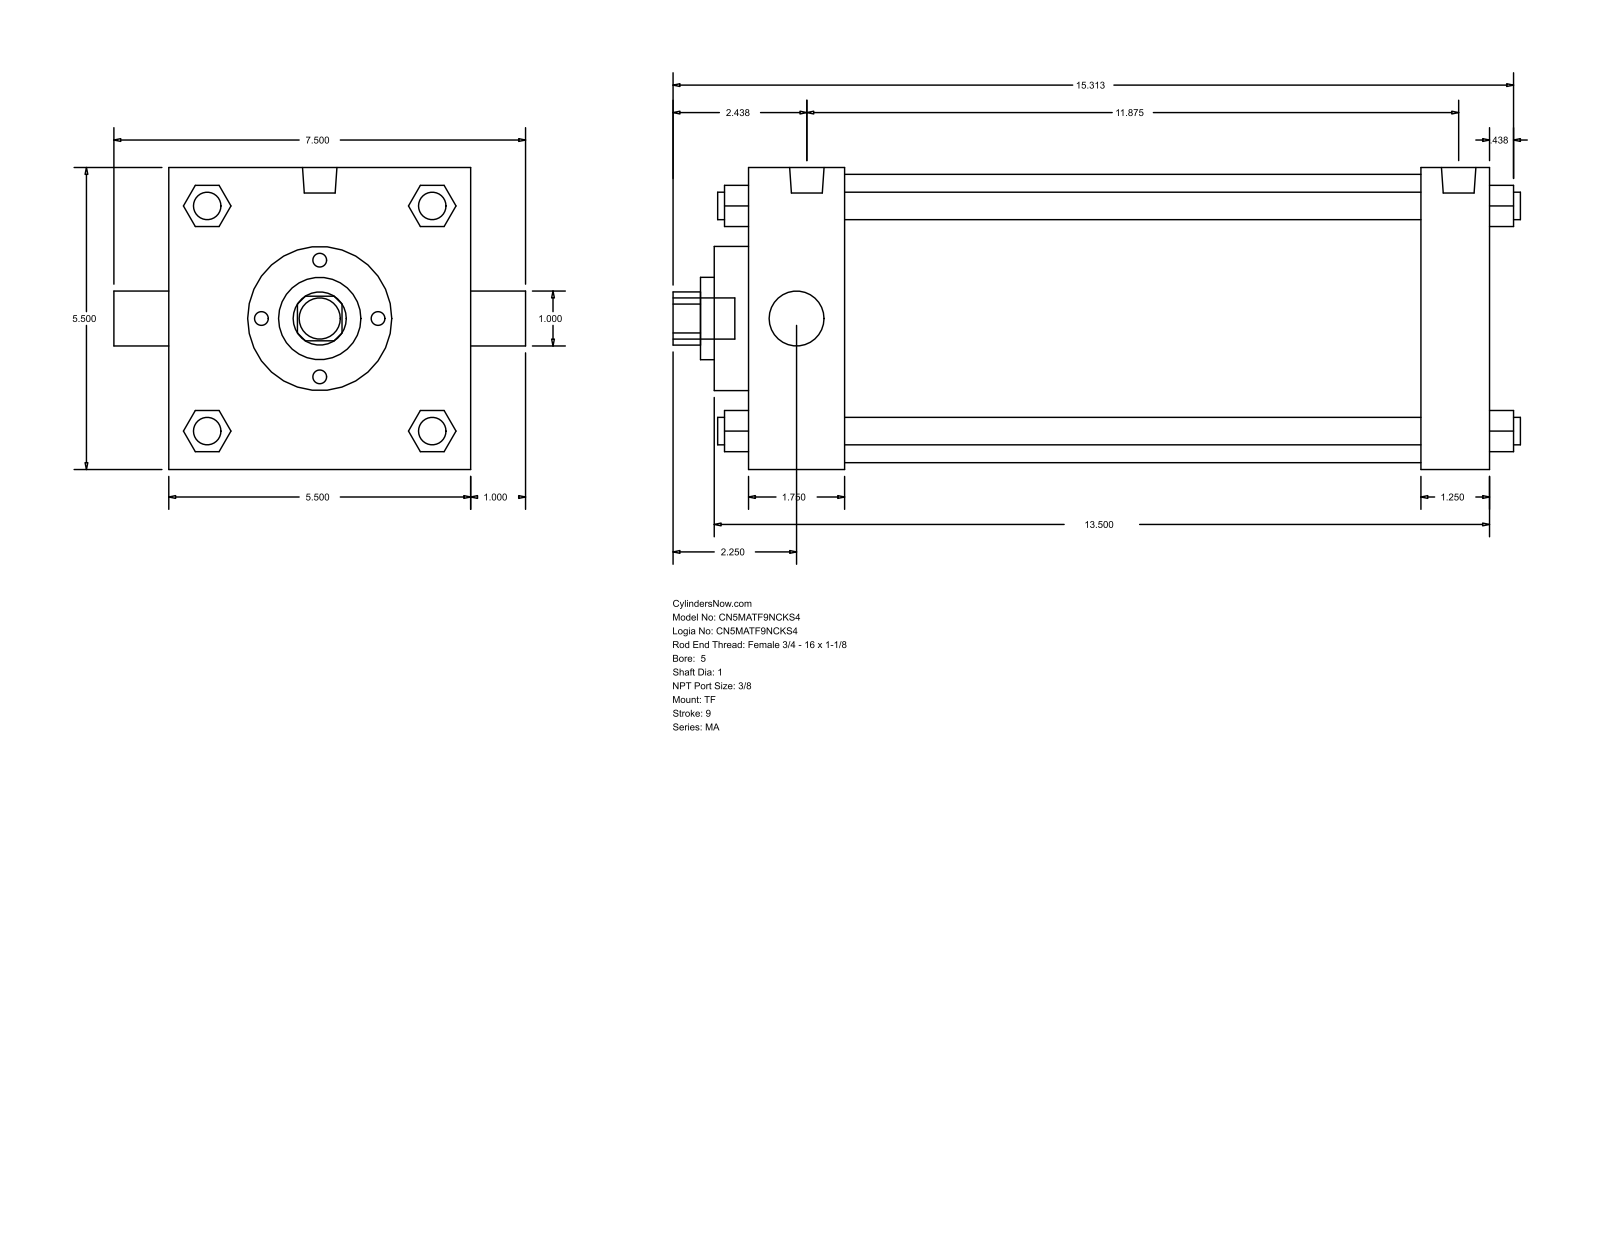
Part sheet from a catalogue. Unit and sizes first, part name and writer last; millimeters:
Units: millimetres
Overall size (bounding box): 392.11 × 190.5 × 139.7
Round holes (diameter × count): ⌀25.4 ×2, ⌀38.1 ×1, ⌀66.67 ×1, ⌀133.35 ×1
Round bosses / shafts (diameter × count): ⌀12.7 ×4, ⌀11.11 ×3, ⌀15.93 ×2, ⌀19.05 ×1
Partial cylindrical surfaces — rounded edges, fillets, slot ends (radius × count): R12.29 ×1
Main face-to-face distances: 139.7, 342.9, 311.15, 31.75, 44.46, 266.69, 298.44, 15.87, 60.33, 327.02
Bodies: 0 solids, 122 faces (93 planar, 29 cylindrical, 0 other)
Part name (STEP PRODUCT): MA_TF__0500_1
STEP written by: GSSL Pune (CONFIG_CONTROL_DESIGN)
